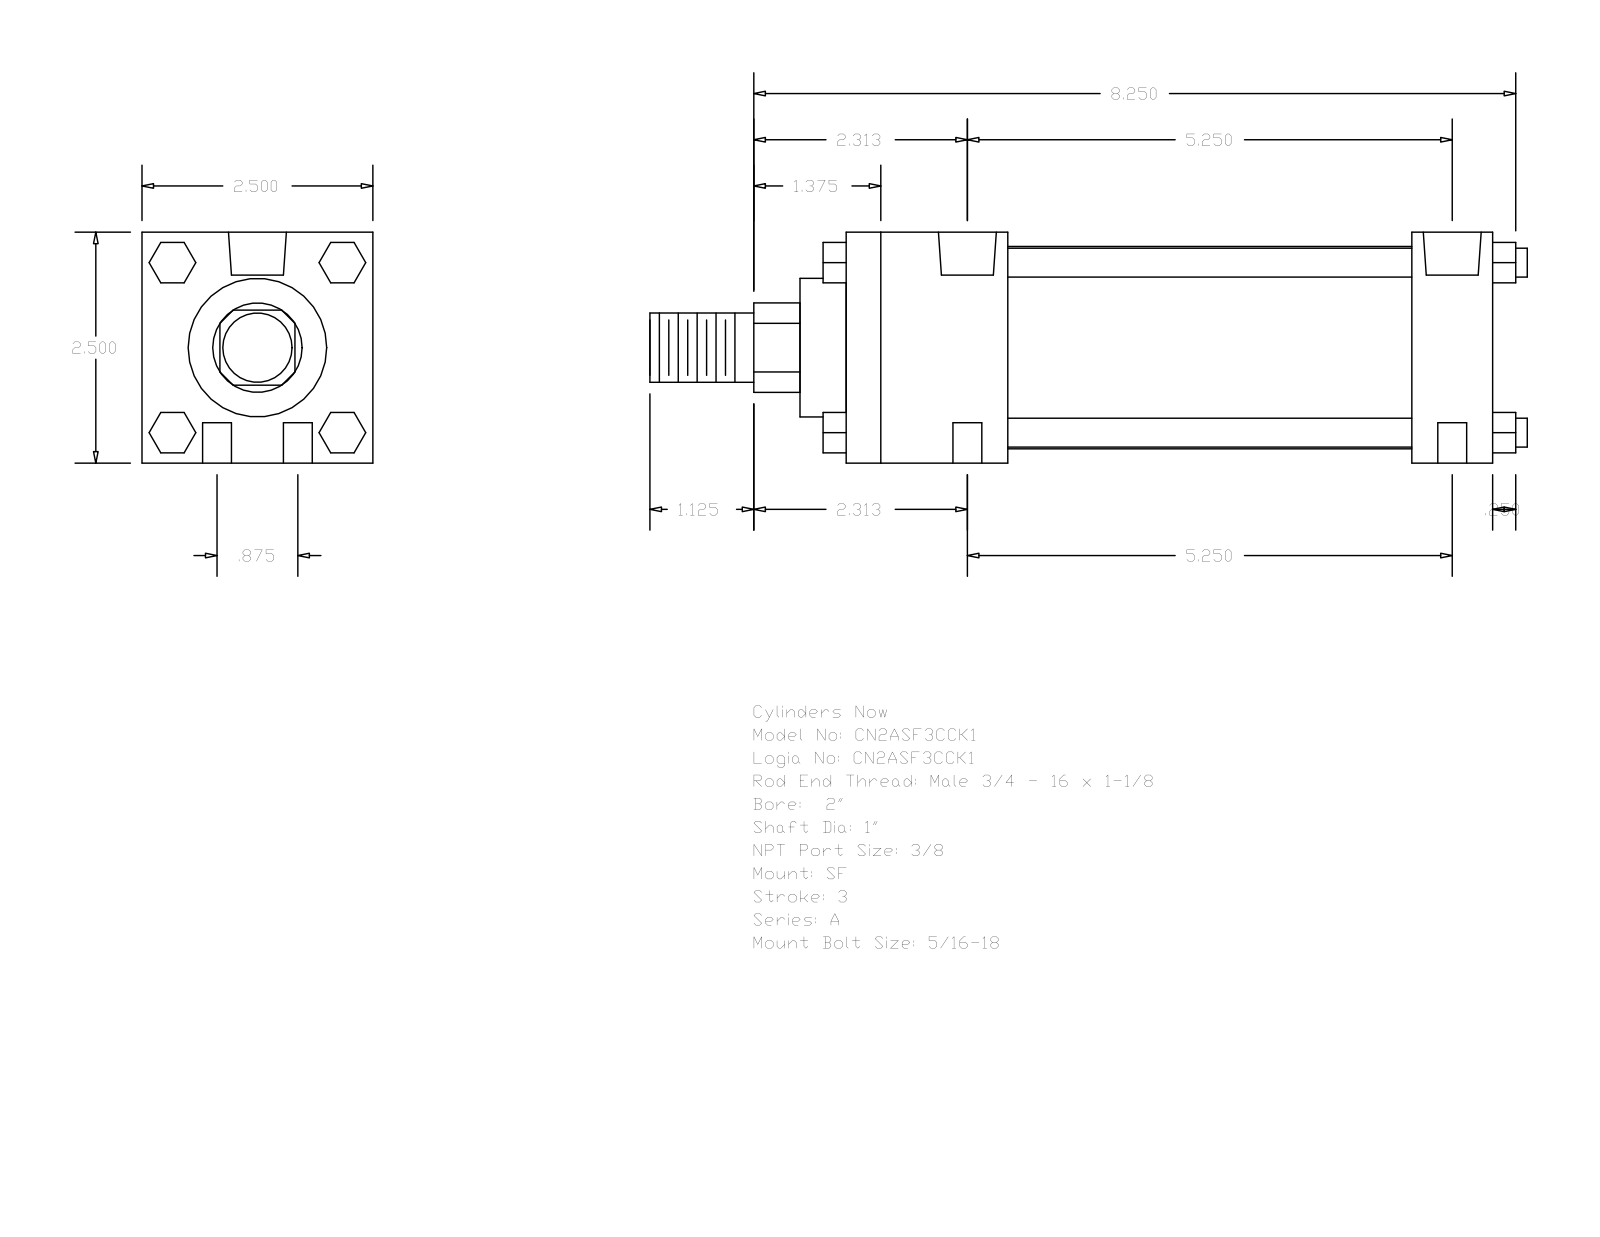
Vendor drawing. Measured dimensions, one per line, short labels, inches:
name: A_SF__0200_1
written by: GSSL Pune (CONFIG_CONTROL_DESIGN)
unit: in
bodies: 0 solids, 124 faces (94 planar, 30 cylindrical, 0 other)
size: 9.5 × 2.5 × 2.5
holes: 4× ⌀0.313, 2× ⌀0.219, 2× ⌀0.627
bosses: 4× ⌀0.313, 1× ⌀2.19, 1× ⌀1.5, 1× ⌀1, 1× ⌀0.75
rounds: 1× R0.484
face distances: 2.5, 7, 6.125, 0.875, 1.75, 4.375, 5.25, 0.5, 7.5, 0.25
hole spacings: 0.437, 5.268, 5.25, 0.875, 5.322, 5.031
